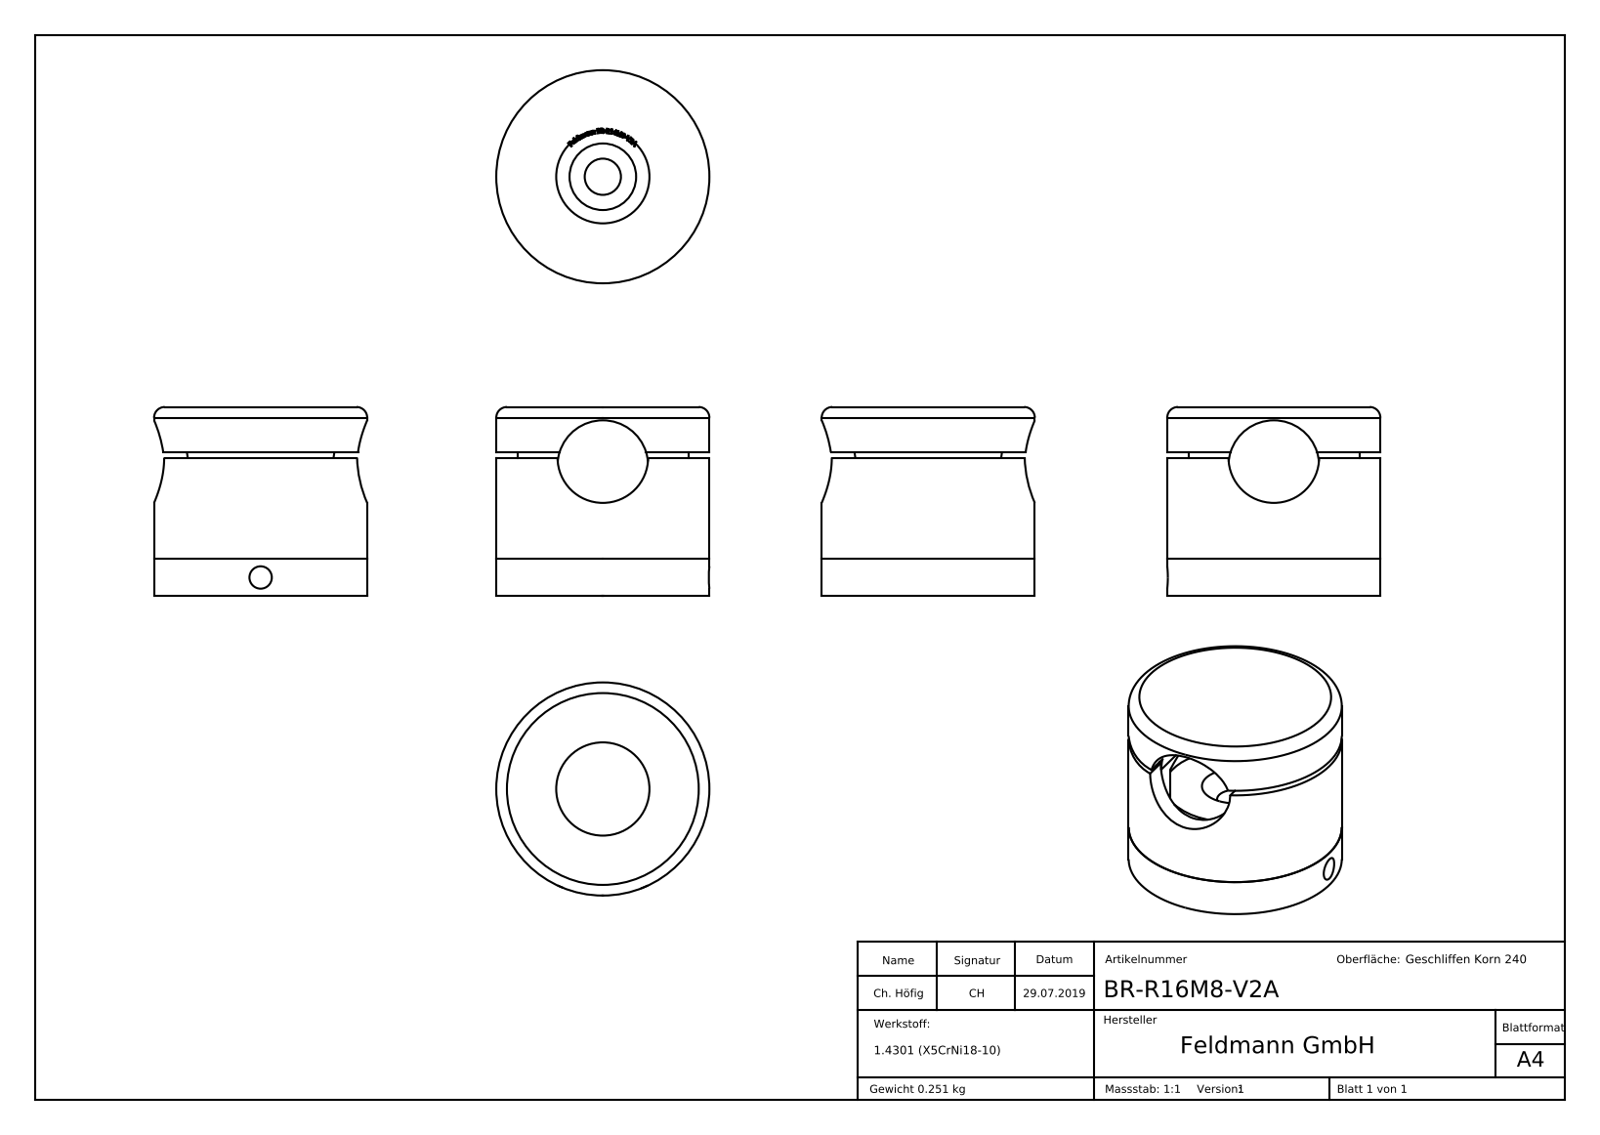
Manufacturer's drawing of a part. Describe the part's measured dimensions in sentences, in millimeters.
The part is named "BR-R16M8-V2A; BR-R1XM8-XXX Teil2_BR-R16M8-V2A Teil2; BR-R1XM8-XXX Teil1_BR-2XM8-V2A Teil1; BR-R1XM8-XXX Teil3 (+3 more)". Its 3-D file was written by "SolidWorks 2015 (CONFIG_CONTROL_DESIGN)". It is 3 solids with 324 faces: 185 planar, 15 cylindrical and 124 other. Overall it measures 64.34 by 40 by 40 millimeters. Its volume is 31 710 cubic millimeters and its surface area 15 148 square millimeters. Round holes: 1 of diameter 4.2, 1 of diameter 6.8, 1 of diameter 12.5, 1 of diameter 32.5. Round bosses or shafts: 1 of diameter 40, 1 of diameter 28. Partial cylindrical surfaces (rounded edges, fillets, slot ends): 2 of radius 8.5, 1 of radius 13.25, 1 of radius 16.05. The main face-to-face distances are 7, 35.5, 28.5, 19.5, 16, 9, 8.5, 27, 20, 11.
